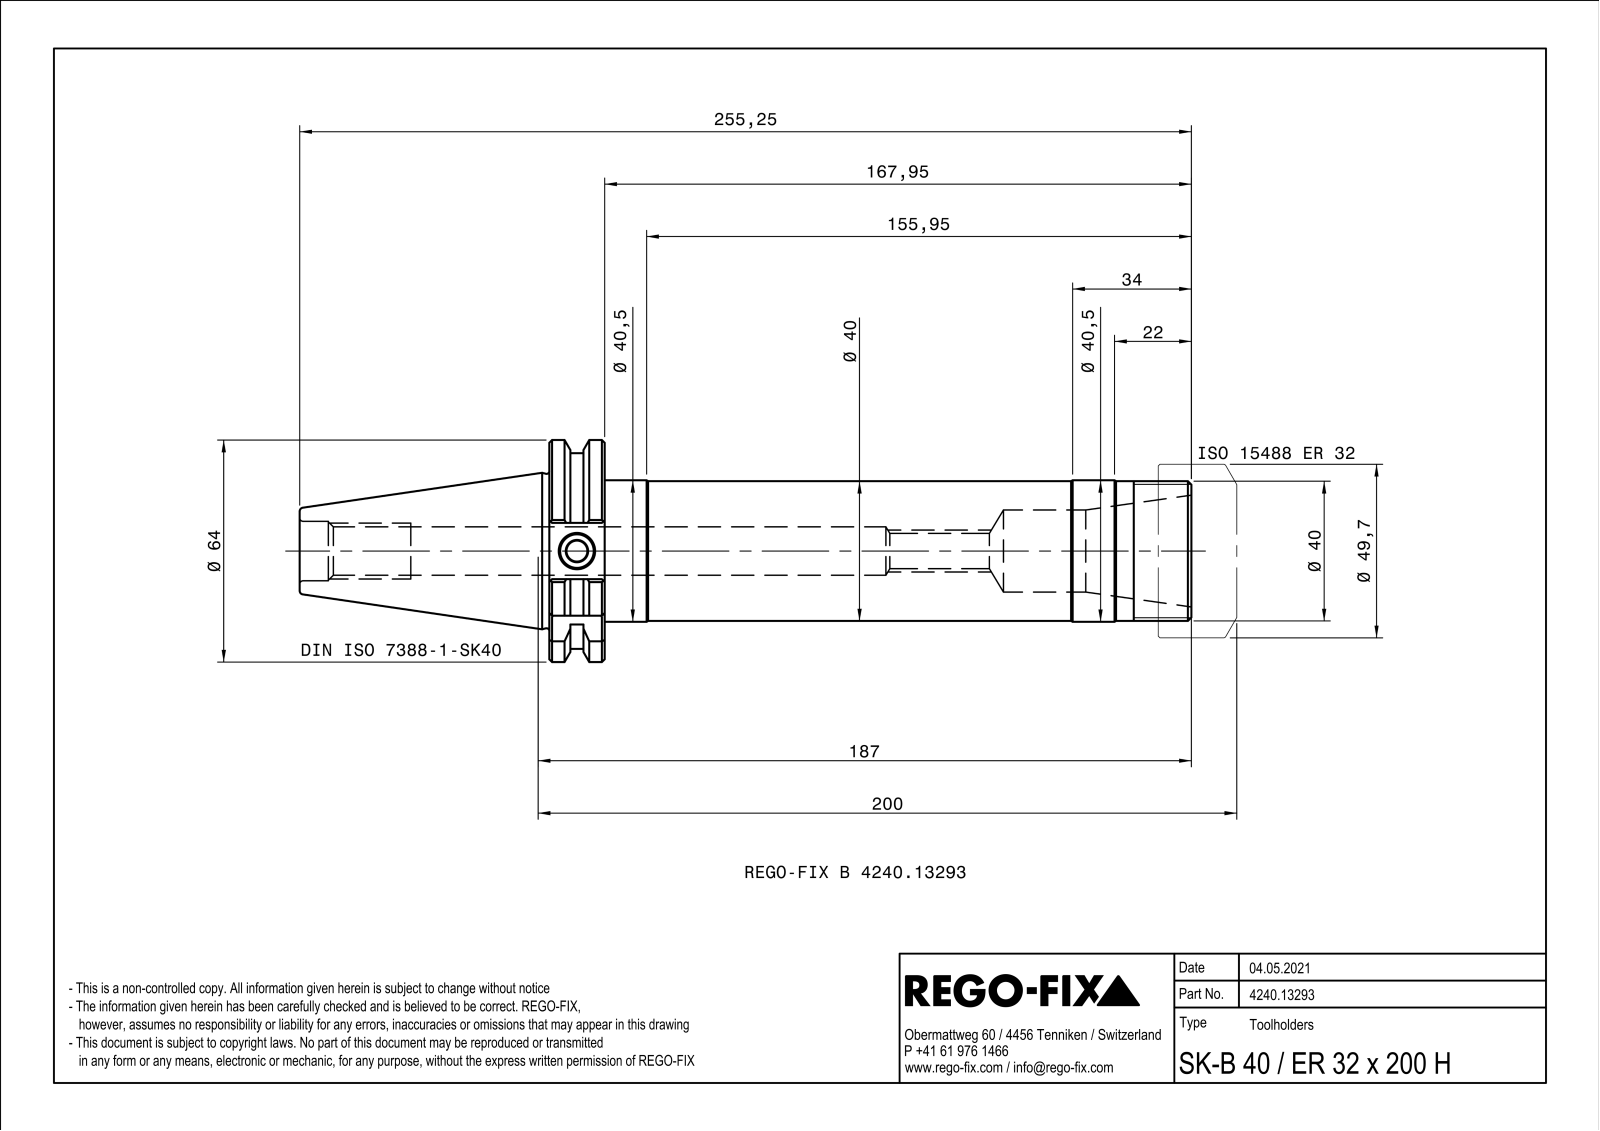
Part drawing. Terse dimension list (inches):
name: NOCUT
written by: SIEMENS PLM Software Solid Edge ST10 (AUTOMOTIVE_DESIGN)
unit: in
bodies: 1 solid, 156 faces (44 planar, 52 cylindrical, 60 other)
size: 10.049 × 2.502 × 2.402
volume: 16.21 in³; area: 78.68 in²
holes: 2× ⌀0.154, 1× ⌀0.128, 1× ⌀0.236, 1× ⌀0.394, 1× ⌀0.398, 1× ⌀0.544, 1× ⌀0.545, 1× ⌀0.669, 1× ⌀0.925
bosses: 1× ⌀1.594, 1× ⌀1.575
rounds: 13× R0.02, 2× R0.089, 1× R1.102, 1× R1.251
face distances: 0.624, 6.612, 7.236, 1.862, 0.634, 10.049, 3.437, 2.813, 0.411, 1.045
